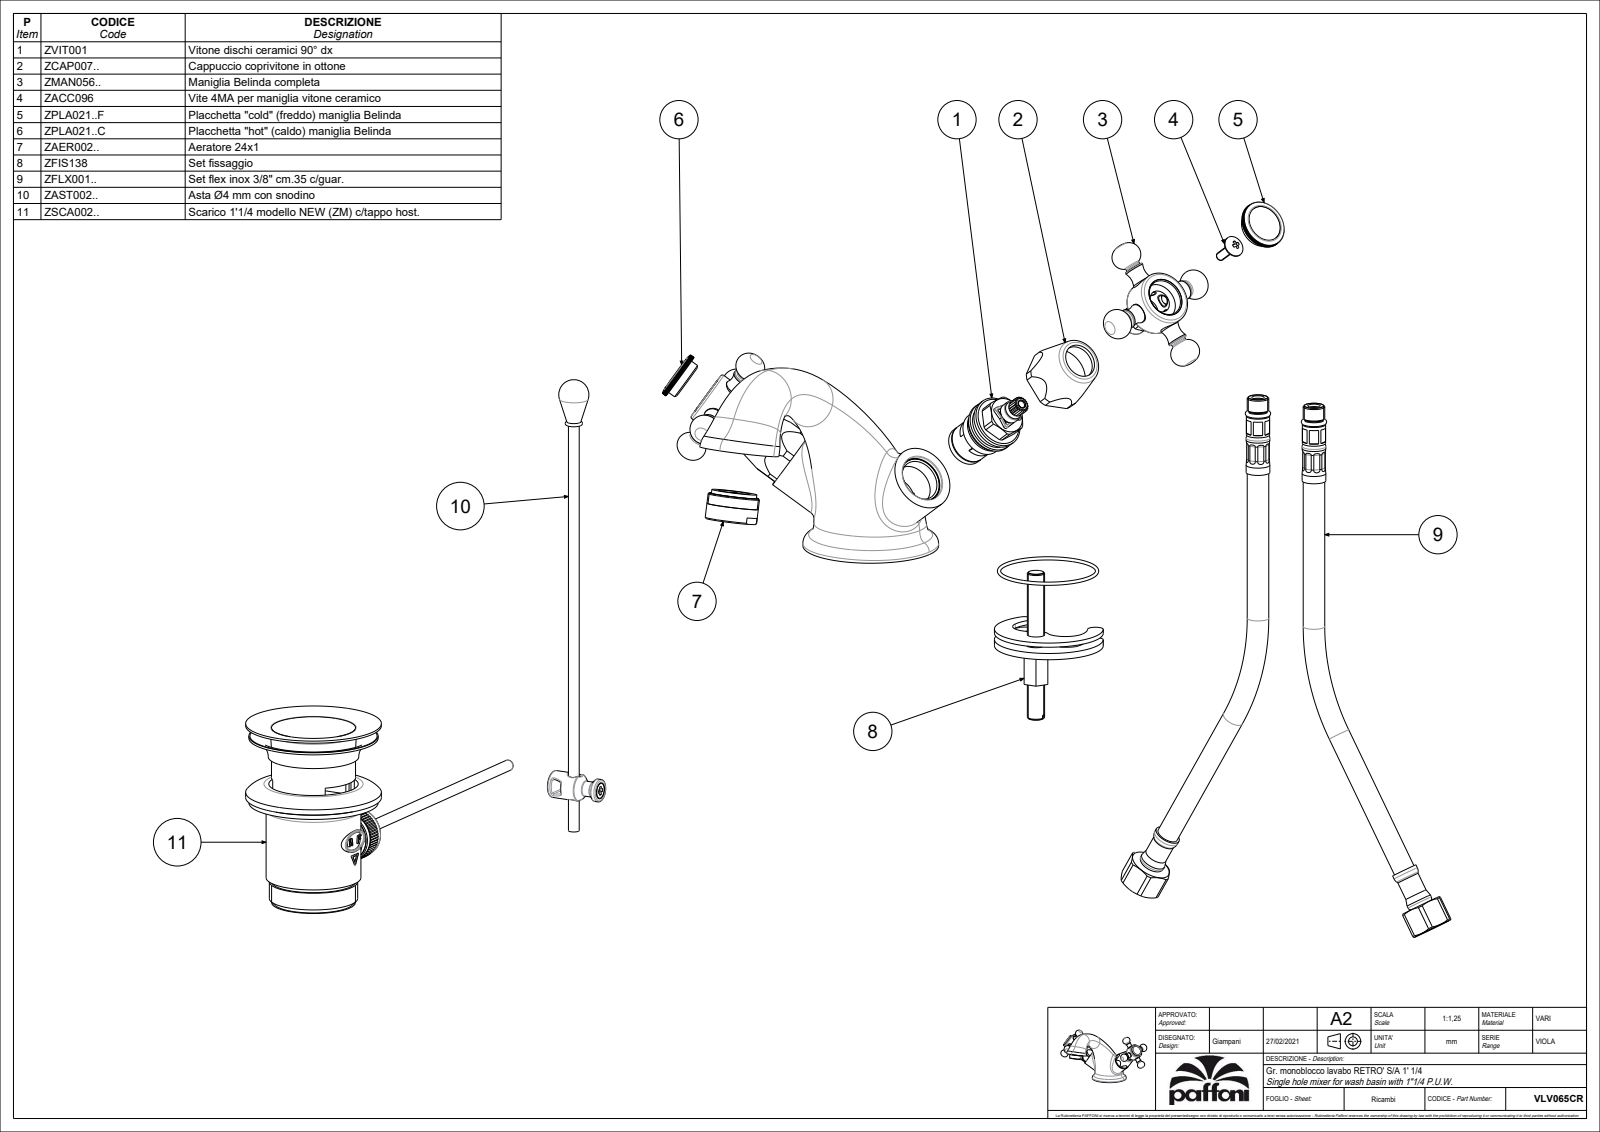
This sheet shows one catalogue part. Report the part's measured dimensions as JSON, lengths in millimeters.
{"part_name": "VLV065CR", "step_written_by": "CREO PARAMETRIC BY PTC INC, 2020044 (CONFIG_CONTROL_DESIGN)", "units": "millimeters", "bodies": {"solids": 1, "faces": 1077, "planar": 513, "cylindrical": 333, "other": 231}, "overall_size": [177.42, 171.45, 106.41], "volume_mm3": 164503, "surface_area_mm2": 64553, "round_holes": [[9, 4], [21, 3], [11, 2], [19, 2], [21.5, 2], [5.5, 1], [6.8, 1], [16.5, 1], [20, 1], [23, 1], [49, 1]], "round_bosses_or_shafts": [[9, 8], [7, 8], [28, 2], [25, 2], [14, 2], [13, 2], [63, 1], [44, 1]], "partial_cylinders_radius": [[11, 2], [14.5, 2], [5, 1]], "face_to_face_distances": [35.33, 21.89, 57.22, 7.7, 1.3, 8.5, 7.82, 5.75, 26.51, 19.01], "hole_center_spacings": [7.5, 12.66, 13.48, 10.2, 11.2, 15, 21.4]}
